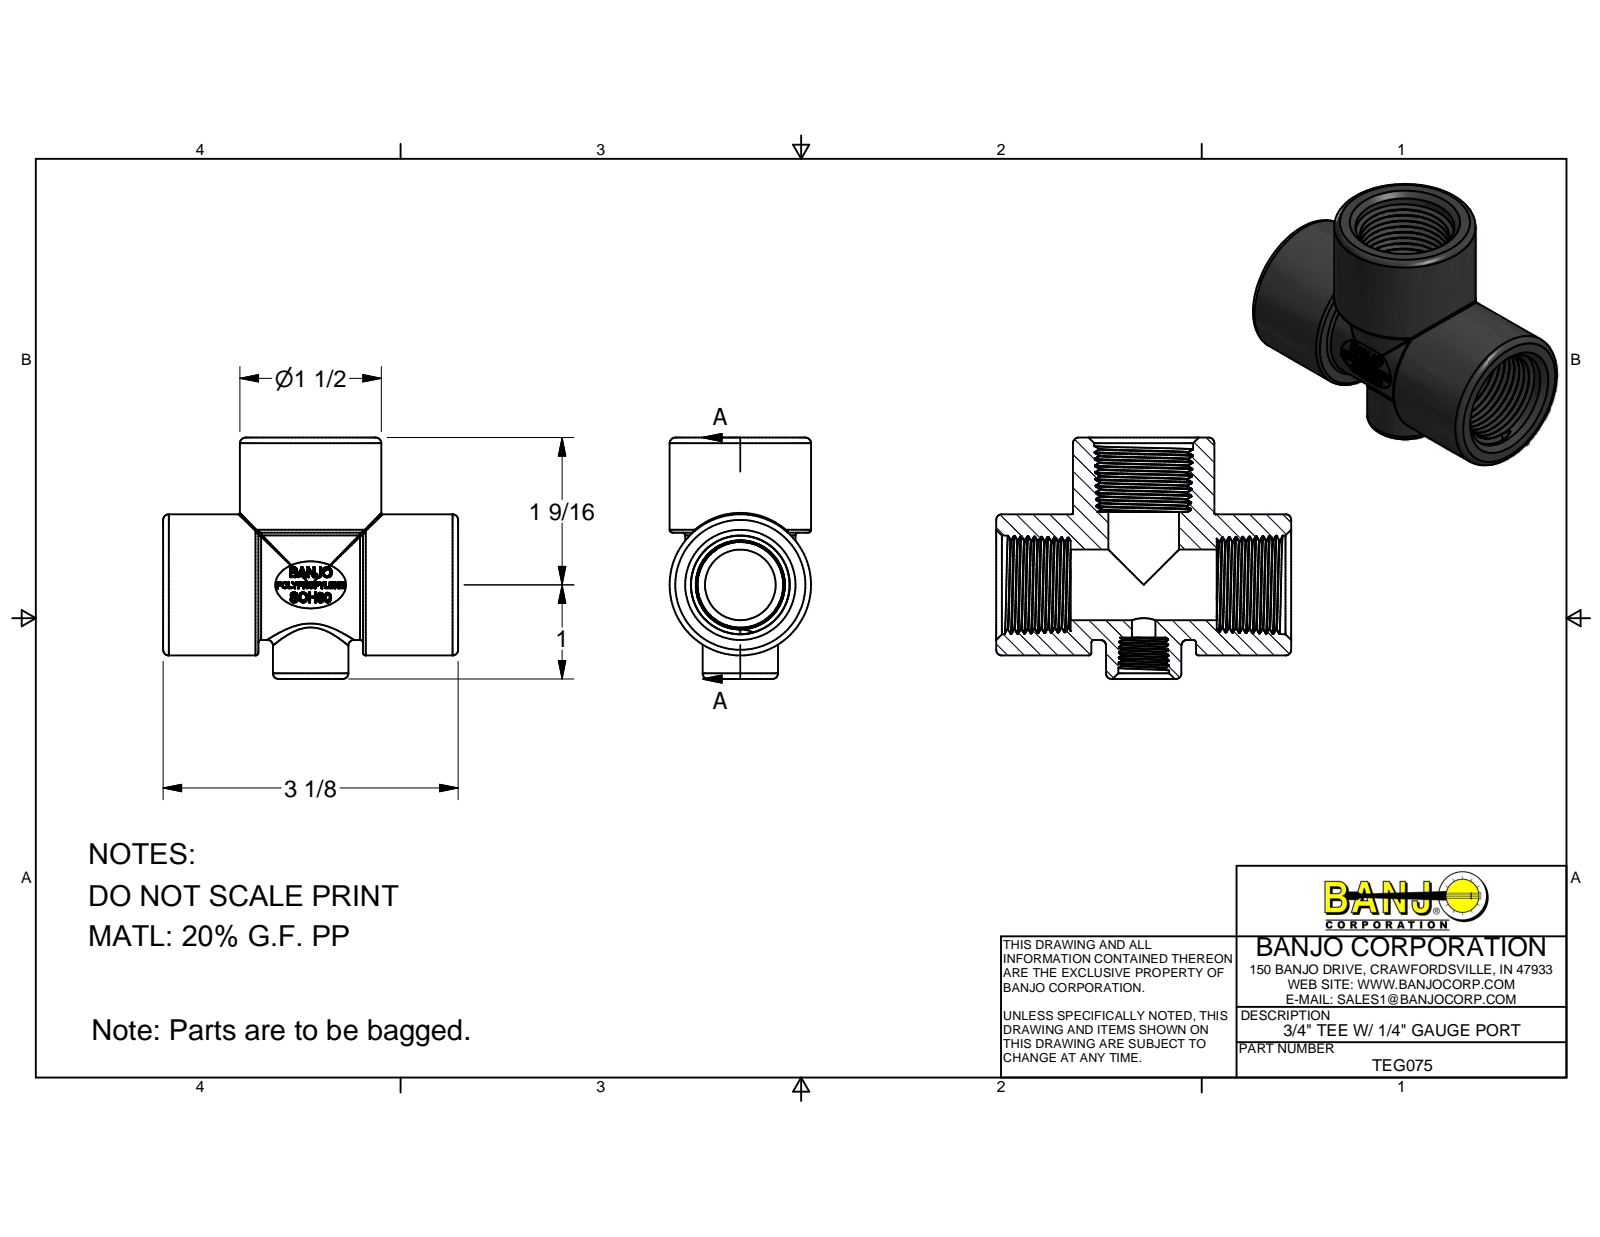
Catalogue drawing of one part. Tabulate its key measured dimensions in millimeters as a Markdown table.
| quantity | value |
| --- | --- |
| part name | TEG075 |
| STEP written by | Autodesk Inventor 2014 (AUTOMOTIVE_DESIGN) |
| units | millimeters |
| bodies | 1 solid, 456 faces (144 planar, 58 cylindrical, 254 other) |
| overall size | 79.5 × 65.15 × 38.1 |
| volume | 64 825 mm³ |
| surface area | 26 012 mm² |
| round holes (diameter × count) | 19.05 × 2, 6.35 × 1 |
| round bosses / shafts (diameter × count) | 38.1 × 2, 29.72 × 1, 20.32 × 1 |
| partial cylindrical surfaces (radius × count) | 7.94 × 3, 0.38 × 2, 14.61 × 2, 4.36 × 1, 14.86 × 1, 15.37 × 1 |
| main face-to-face distances | 25.65, 20.07, 5.58, 53.85, 59.43, 33.78, 79.5, 28.2, 39.36, 28.32 |
